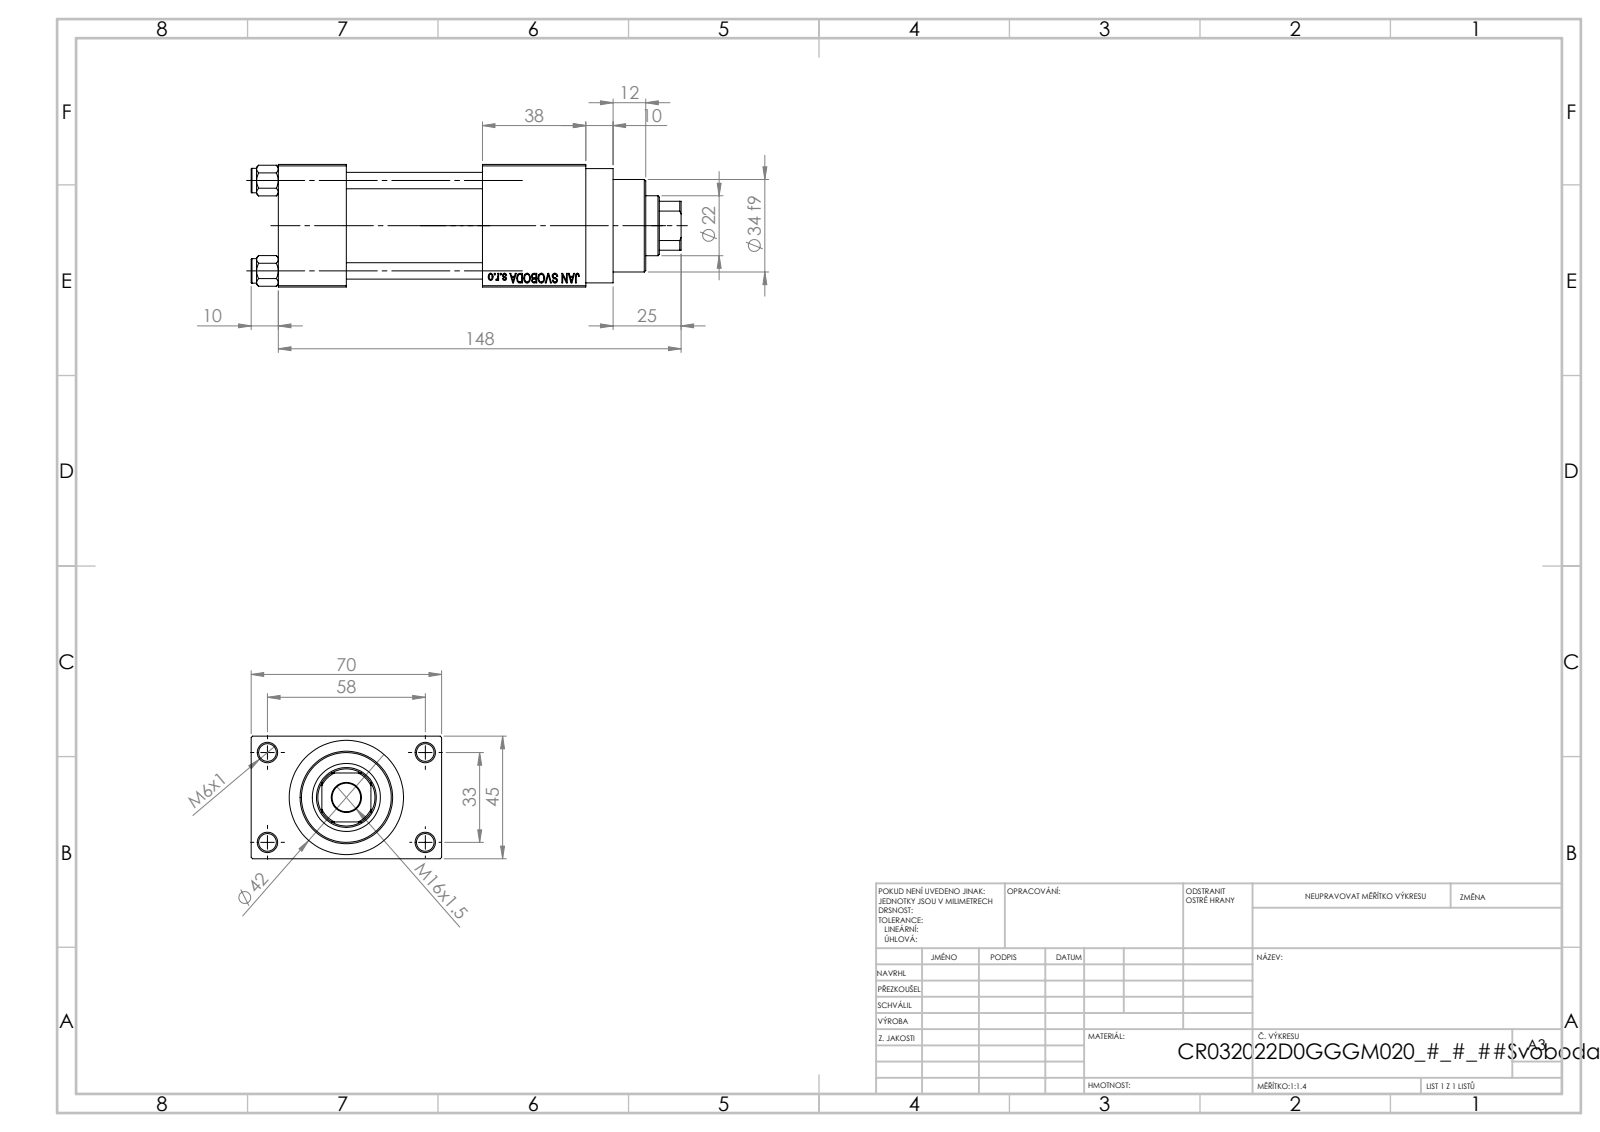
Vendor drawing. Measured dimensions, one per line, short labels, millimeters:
name: V215CR_VCP_D; V215CR_D_TYCINKA; V215_VC_A; V215CR_D_Body (+1 more)
written by: SolidWorks 2019 (CONFIG_CONTROL_DESIGN)
unit: mm
bodies: 11 solids, 1103 faces (496 planar, 89 cylindrical, 518 other)
size: 158 × 70 × 45
volume: 244 616 mm³; area: 79 456 mm²
holes: 4× ⌀6, 4× ⌀6.5, 2× ⌀7, 2× ⌀13.16, 2× ⌀20, 1× ⌀10.5, 1× ⌀22, 1× ⌀24, 1× ⌀25, 1× ⌀32, 1× ⌀33
bosses: 4× ⌀9, 1× ⌀42, 1× ⌀38, 1× ⌀34
rounds: 1× R10.5
face distances: 45, 25, 12.5, 57.5, 50, 75, 88, 70, 38, 113
hole spacings: 12.4, 23.48, 33.2, 33.37, 35.35, 45.6, 56.35, 33
